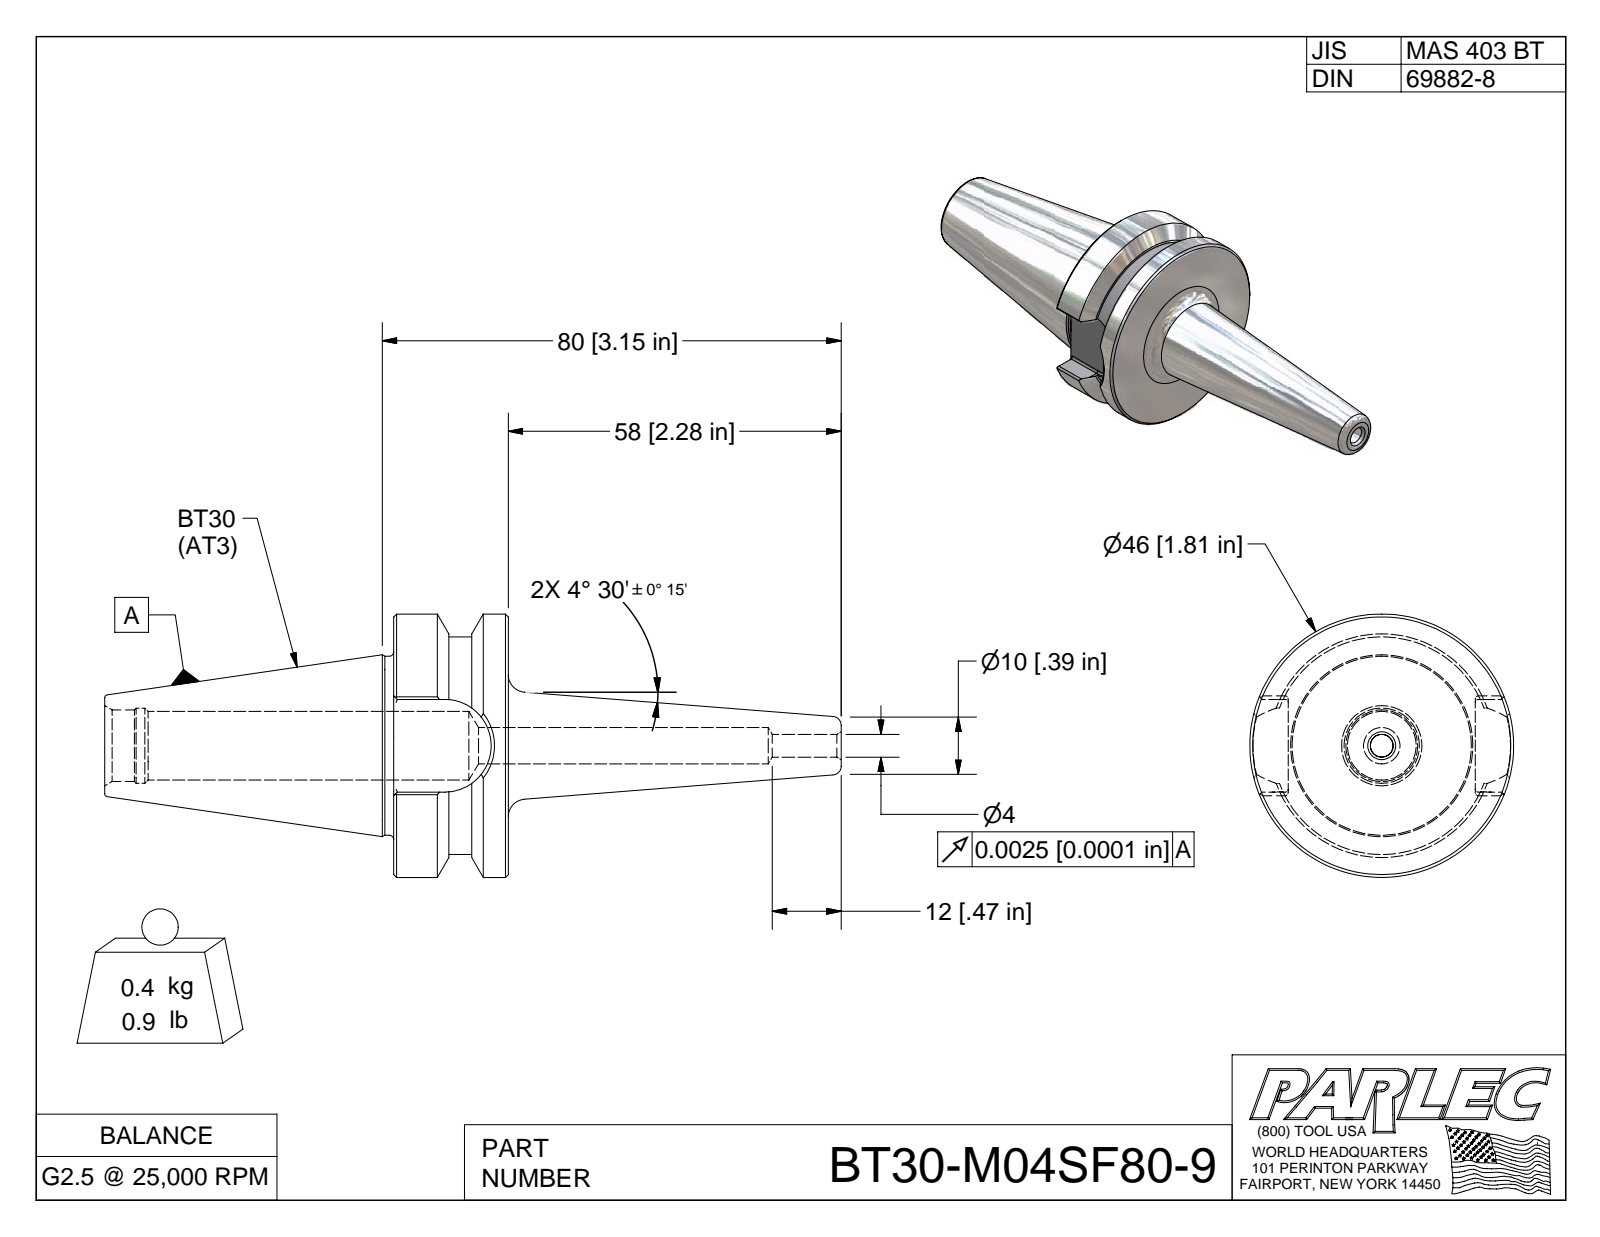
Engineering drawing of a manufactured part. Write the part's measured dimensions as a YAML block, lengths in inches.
part_name: "BT30-M04SF80-9; BT30-M04SF80-9-1"
step_written_by: "Autodesk Inventor 2009 (AUTOMOTIVE_DESIGN)"
units: inches
bodies: {solids: 1, faces: 69, planar: 24, cylindrical: 18, other: 27}
overall_size: [5.056, 1.811, 1.811]
volume: 3.294
surface_area: 24.76
round_holes:
  - {diameter: 0.157, count: 1}
  - {diameter: 0.517, count: 1}
round_bosses_or_shafts:
  - {diameter: 1.811, count: 1}
  - {diameter: 1.23, count: 1}
partial_cylinders:
  - {radius: 0.02, count: 8}
  - {radius: 0.319, count: 1}
  - {radius: 0.748, count: 1}
face_to_face_distances: [0.787, 1.283, 1.984, 2.771, 0.637, 2.52, 0.536, 0.251, 2.363, 0.379]
